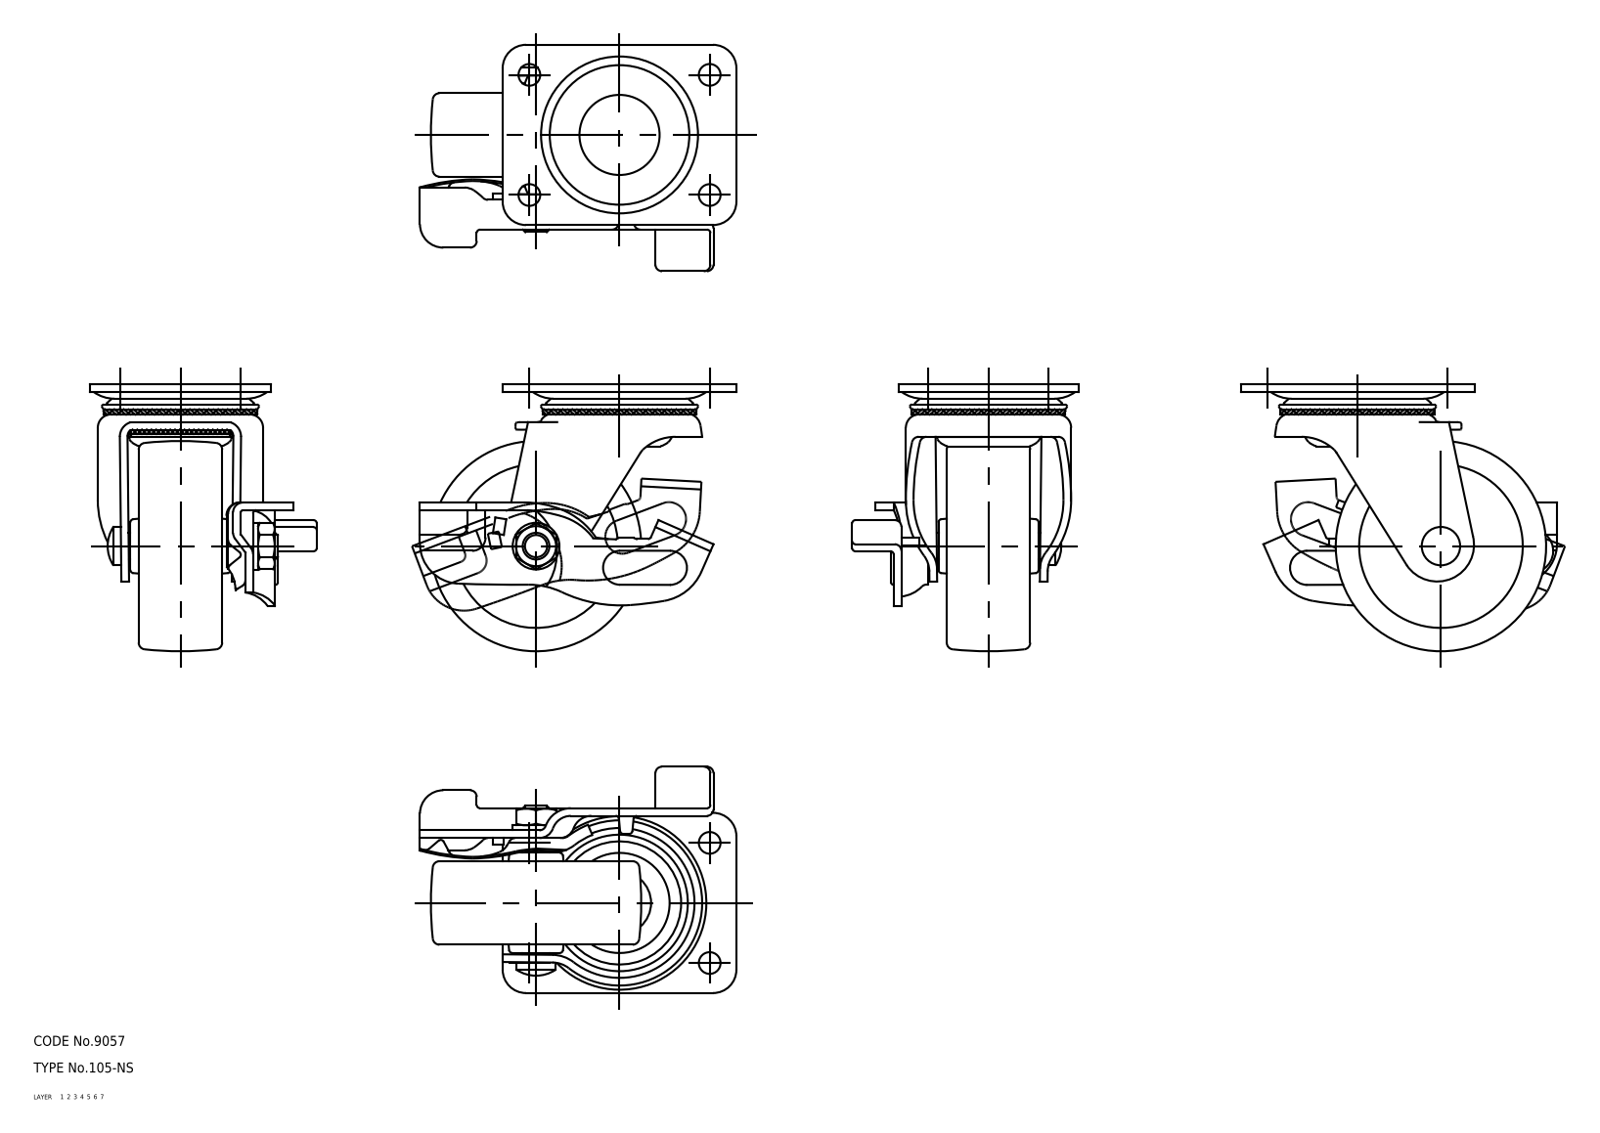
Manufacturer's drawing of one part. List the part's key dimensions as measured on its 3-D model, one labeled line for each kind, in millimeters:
Part name (STEP PRODUCT): plate; wheel; lever; axle (+3 more)
STEP written by: CADfix (AUTOMOTIVE_DESIGN)
Units: millimetres
Bodies: 7 solids, 443 faces (0 planar, 0 cylindrical, 443 other)
Overall size (bounding box): 94.76 × 80 × 67.83
Volume: 95 268 mm³ · Surface area: 46 532 mm²
